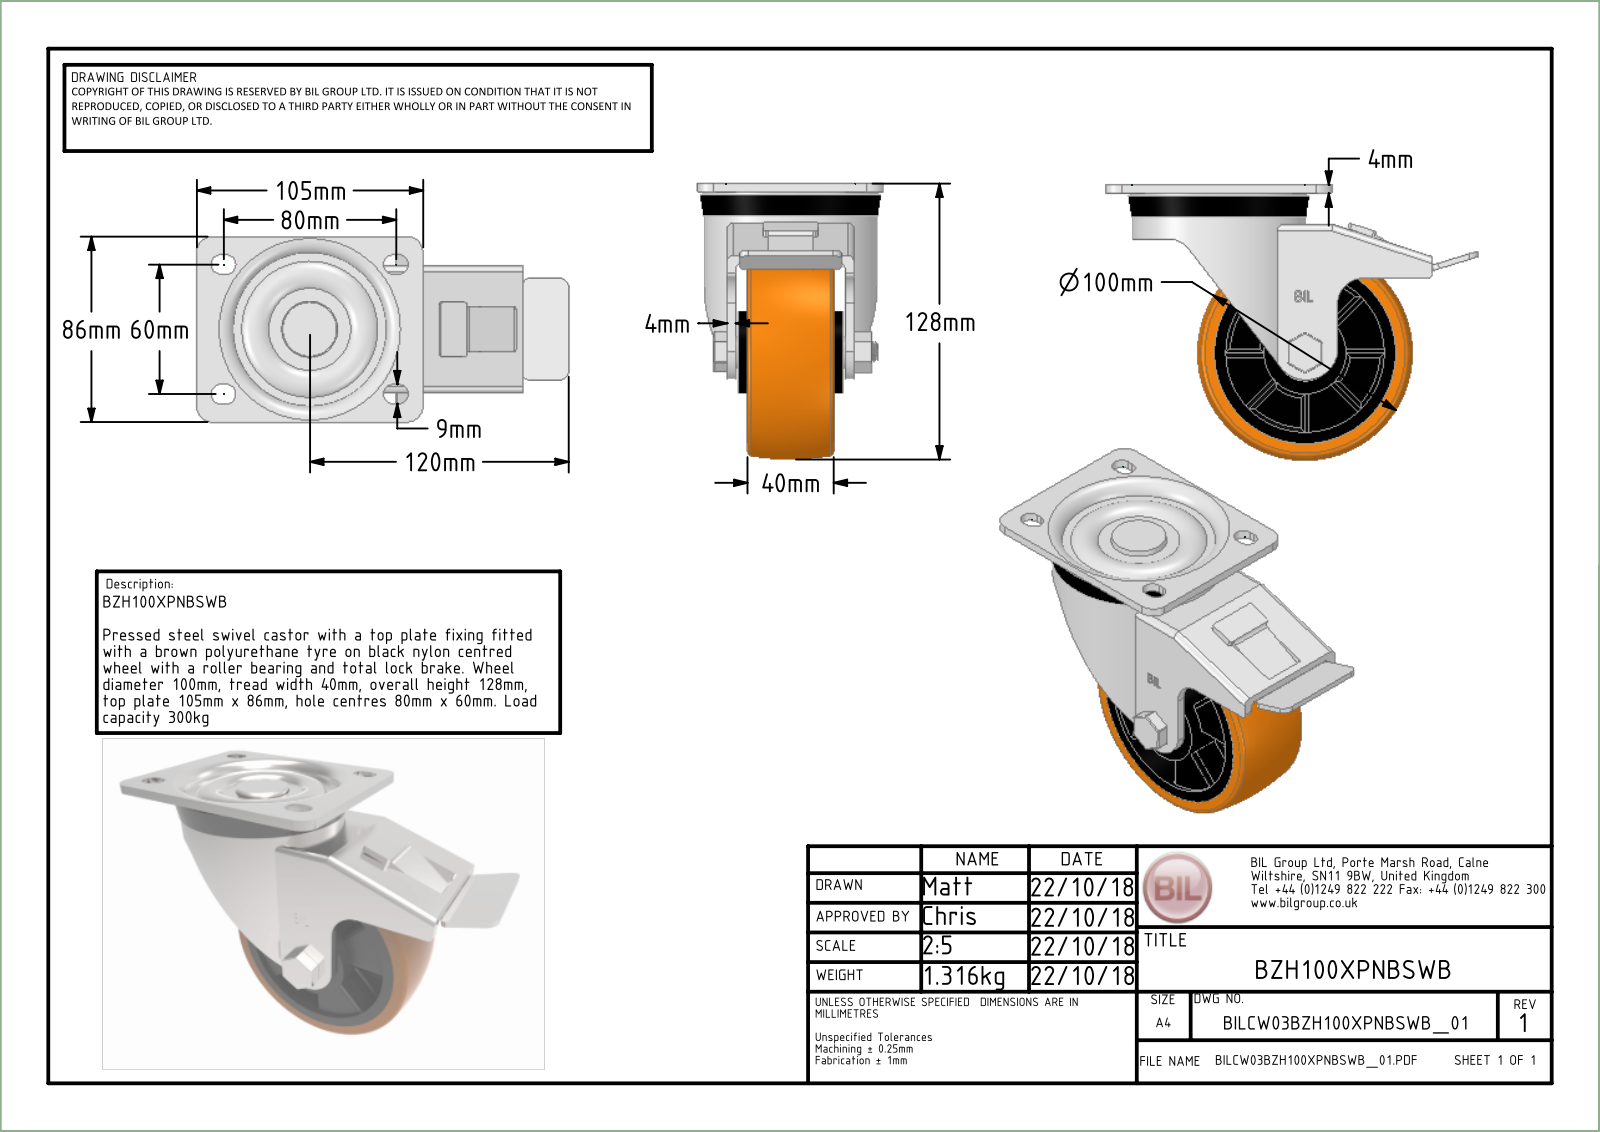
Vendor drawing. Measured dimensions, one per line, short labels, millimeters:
name: BZH100XPNBSWB v3; BZH100ASSWB v1; ZINC PLATED, PRESSED STEEL TOP PLATE; ZINC PLATED, PRESSED STEEL FORKS (+8 more)
written by: Autodesk Translation Framework v14.10.0.0 (AUTOMOTIVE_DESIGN)
unit: mm
bodies: 22 solids, 896 faces (400 planar, 226 cylindrical, 270 other)
size: 172.5 × 128 × 86
volume: 379 834 mm³; area: 170 191 mm²
holes: 1× ⌀6, 1× ⌀10, 1× ⌀10.2, 1× ⌀10.3, 1× ⌀12, 1× ⌀15, 1× ⌀15.5, 1× ⌀25, 1× ⌀26, 1× ⌀27, 1× ⌀32, 1× ⌀72
bosses: 8× ⌀4, 1× ⌀80, 1× ⌀60, 1× ⌀37, 1× ⌀31, 1× ⌀26.9, 1× ⌀22.5, 1× ⌀20
rounds: 27× R0.5, 18× R2, 10× R4, 8× R4.5, 6× R0.75, 6× R1.5, 4× R8, 3× R1
face distances: 4, 5, 1, 9.5, 5.5, 11.5, 49.5, 7.5, 10.5, 2.5
